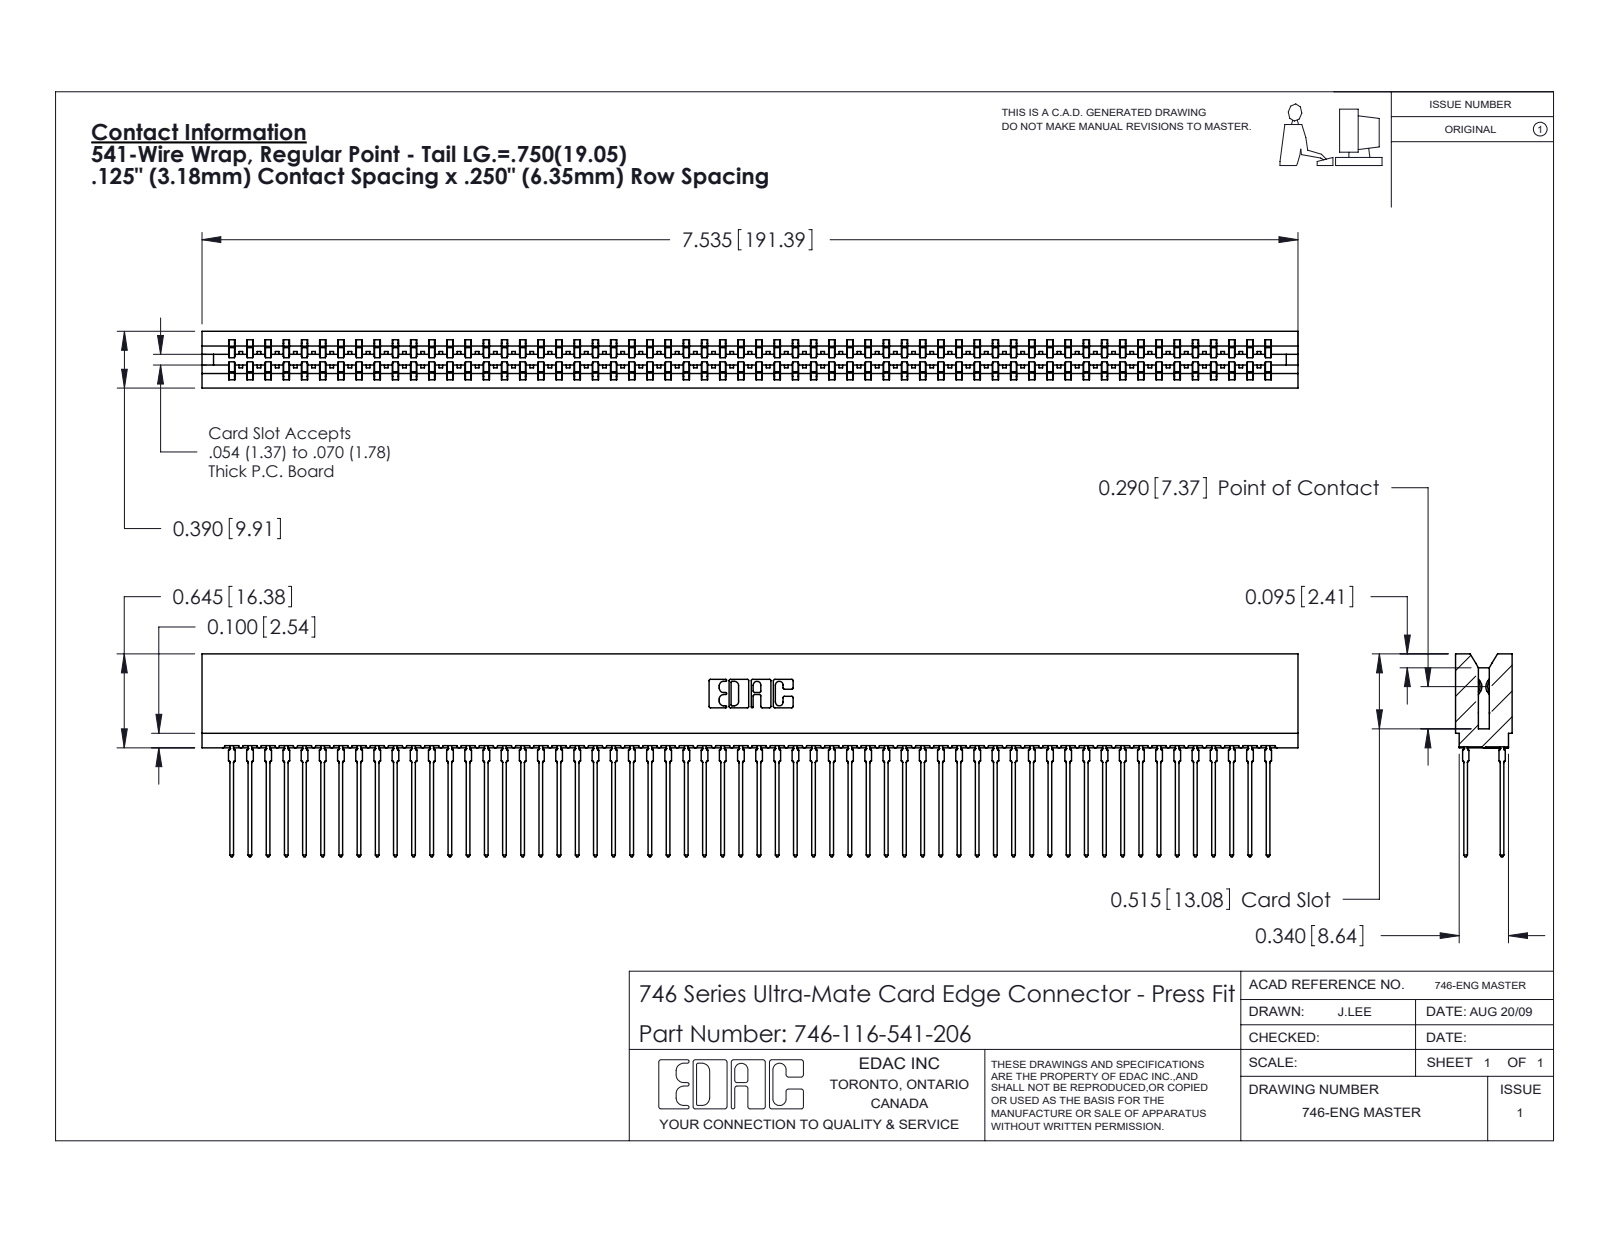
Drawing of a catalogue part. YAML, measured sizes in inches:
part_name: "746 Part_.515 Slot Depth - 06; 746-292-001_541; 746-116-541-206"
step_written_by: "SolidWorks 2020 (CONFIG_CONTROL_DESIGN)"
units: inches
bodies: {solids: 117, faces: 10480, planar: 5392, cylindrical: 2072, other: 3016}
overall_size: [7.535, 1.394, 0.39]
volume: 1.283
surface_area: 57.47
partial_cylinders:
  - {radius: 0.021, count: 232}
  - {radius: 0.015, count: 59}
  - {radius: 0.01, count: 22}
  - {radius: 0.005, count: 8}
  - {radius: 0.011, count: 8}
  - {radius: 0.007, count: 6}
  - {radius: 0.031, count: 6}
  - {radius: 0.026, count: 3}
face_to_face_distances: [0.057, 0.333, 0.25, 0.025, 0.307, 0.39, 0.083, 0.275, 0.174, 0.158]
